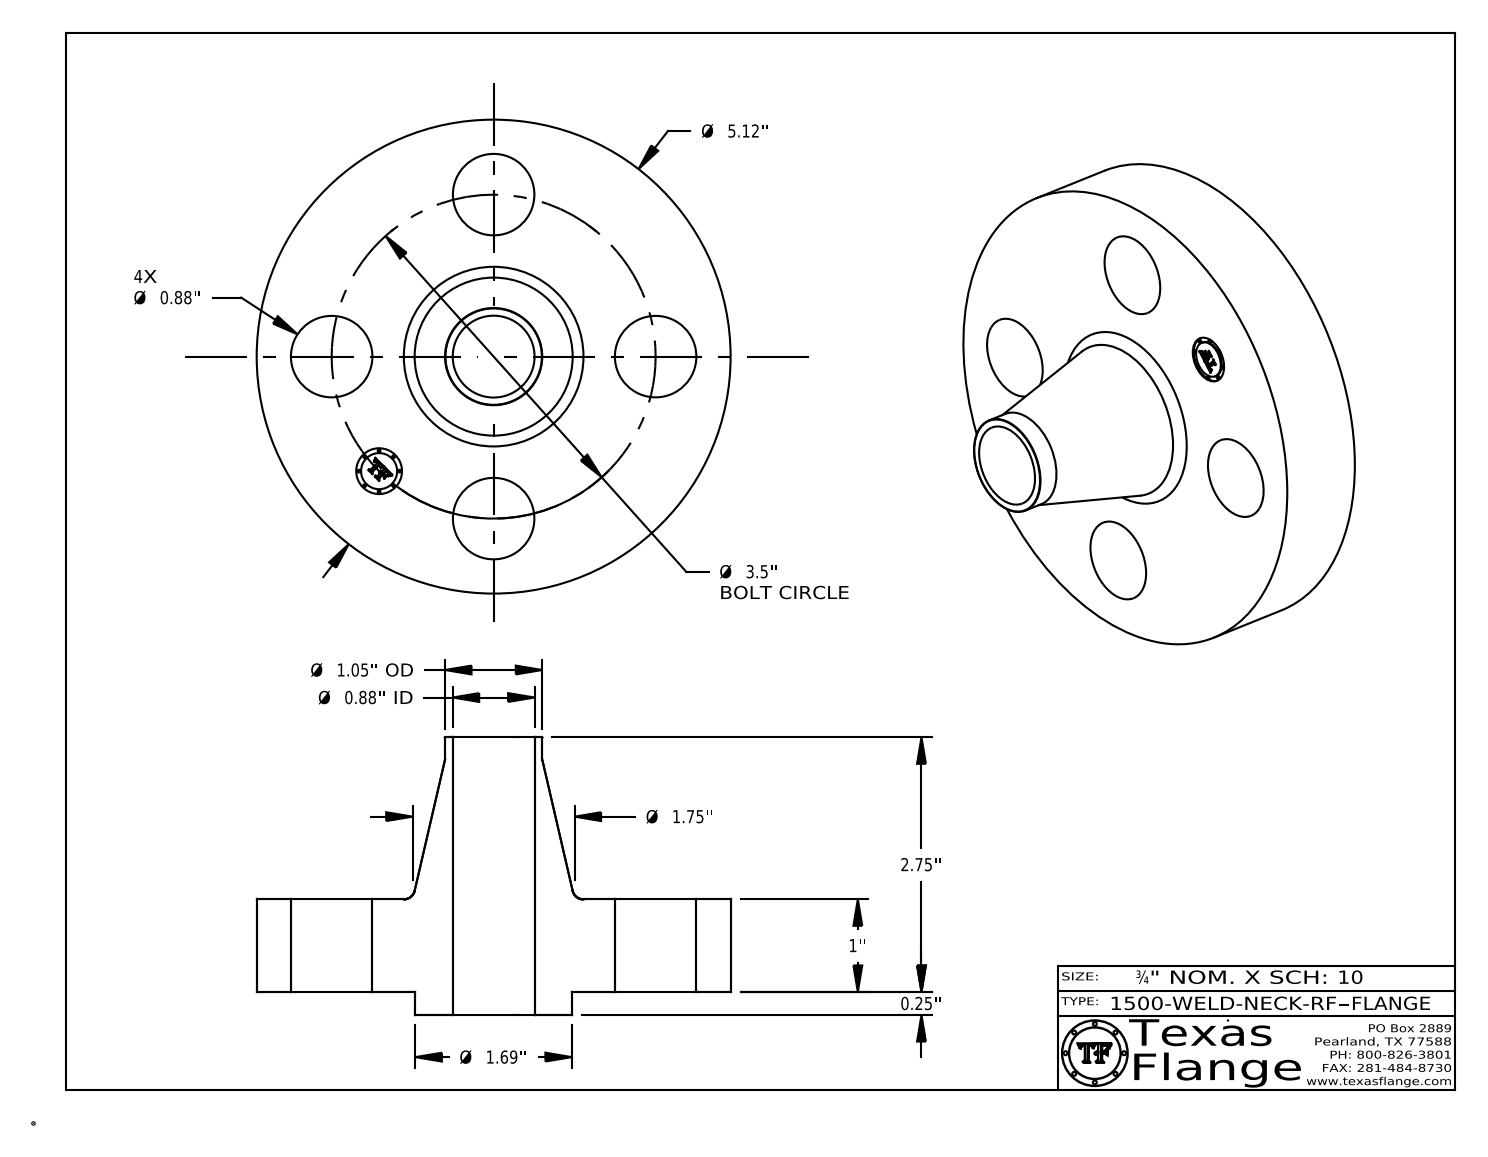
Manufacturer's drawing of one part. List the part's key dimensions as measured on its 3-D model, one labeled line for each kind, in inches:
Part name (STEP PRODUCT): 1500-WELD-NECK-RF
STEP written by: CATIA V5 STEP AP214 (AUTOMOTIVE_DESIGN)
Units: inches
Bodies: 1 solid, 411 faces (369 planar, 36 cylindrical, 6 other)
Overall size (bounding box): 5.12 × 5.12 × 3
Volume: 19.47 in³ · Surface area: 77.88 in²
Round holes (diameter × count): ⌀0.88 ×4, ⌀0.495 ×1, ⌀0.884 ×1
Round bosses / shafts (diameter × count): ⌀0.03 ×8, ⌀5.12 ×1, ⌀1.69 ×1, ⌀1.05 ×1, ⌀0.39 ×1
Main face-to-face distances: 1, 0.25, 1.25, 3, 2.75, 1.75, 0.015, 1.235, 0.985, 1.765
Hole centre spacings: 1.75, 2.475, 1.339, 3.233, 3.5
